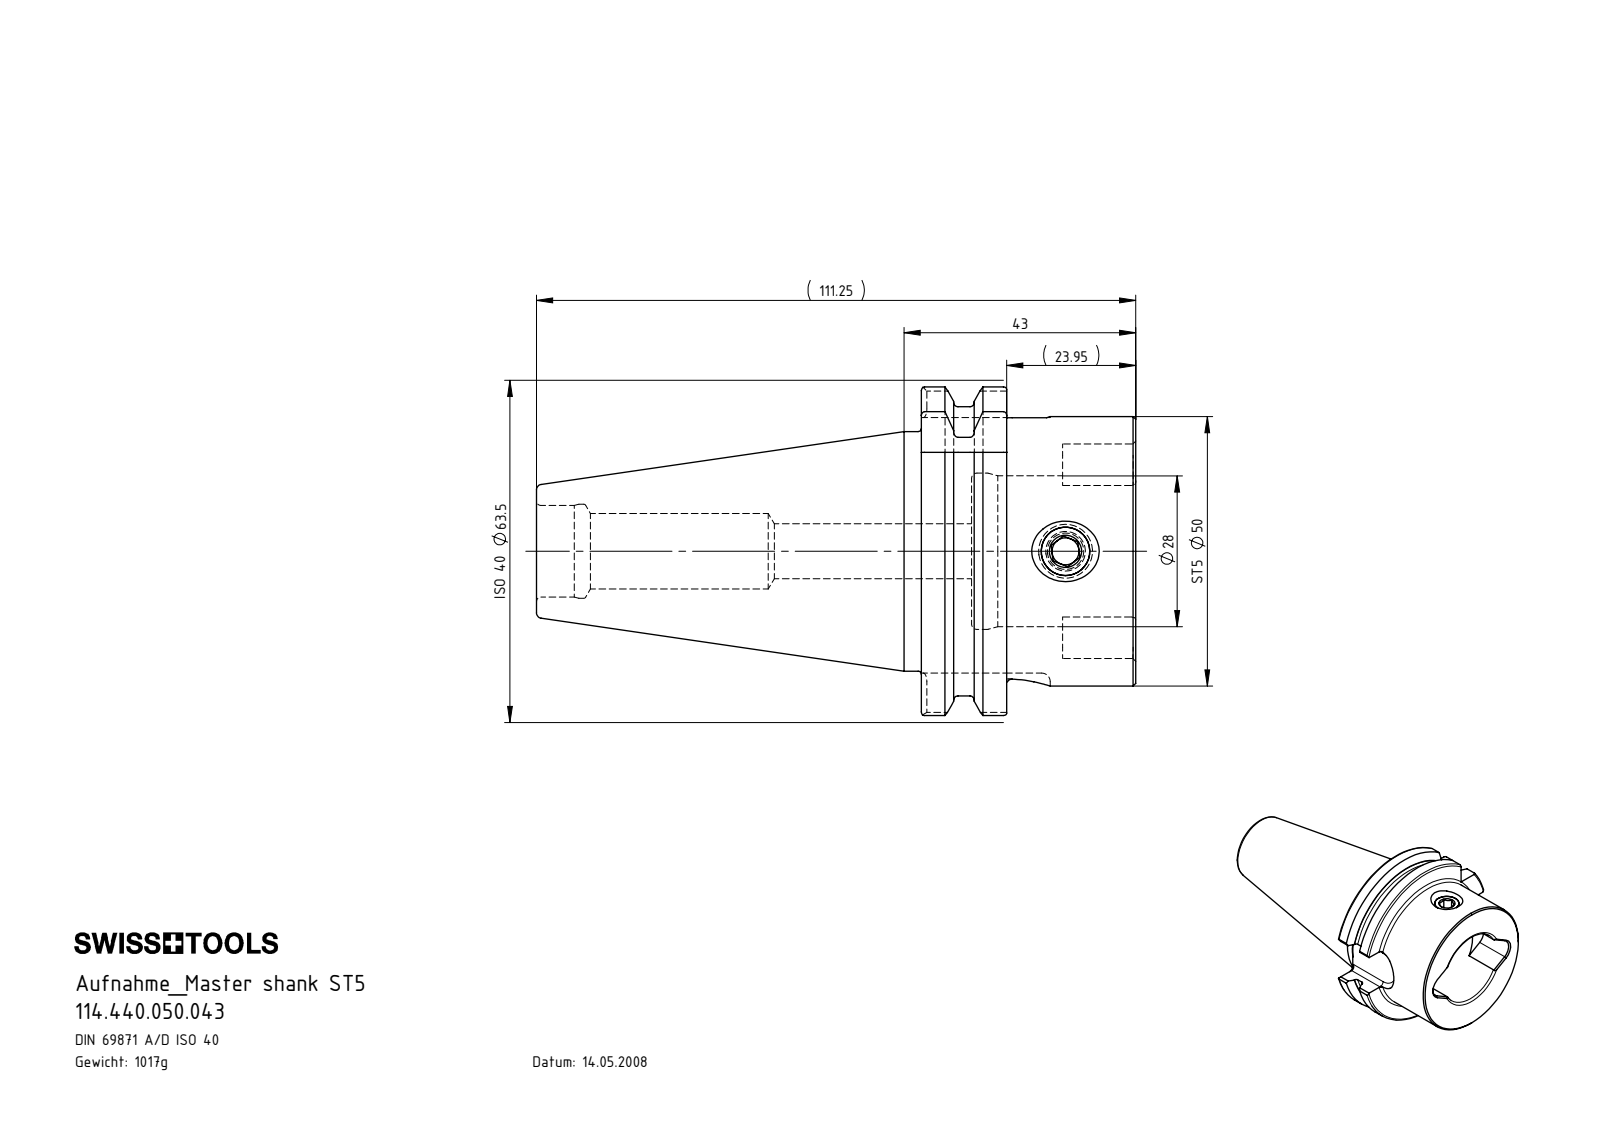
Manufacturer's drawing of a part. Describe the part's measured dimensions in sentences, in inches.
The part is named "SK4-ST5.K01.043_B; SK4.ST5.K01.043; ST5-ER1.001.012_A". Its 3-D file was written by "SolidWorks 2017 (AUTOMOTIVE_DESIGN)". It is 2 solids with 132 faces: 56 planar, 32 cylindrical and 44 other. Overall it measures 4.38 by 2.5 by 2.399 inches. Its volume is 7.906 cubic inches and its surface area 41.69 square inches. Round holes: 1 of diameter 0.197, 1 of diameter 0.354, 1 of diameter 0.402, 1 of diameter 0.551, 1 of diameter 0.669, 1 of diameter 0.687, 1 of diameter 1.102, 1 of diameter 1.142. Round bosses or shafts: 1 of diameter 1.969, 1 of diameter 1.75, 1 of diameter 0.394. Partial cylindrical surfaces (rounded edges, fillets, slot ends): 8 of radius 0.063, 2 of radius 0.165, 1 of radius 0.317, 1 of radius 1.102, 1 of radius 1.25. The main face-to-face distances are 1.567, 0.624, 0.943, 0.366, 0.258, 1.201, 1.866, 0.949, 2.813, 3.179.
